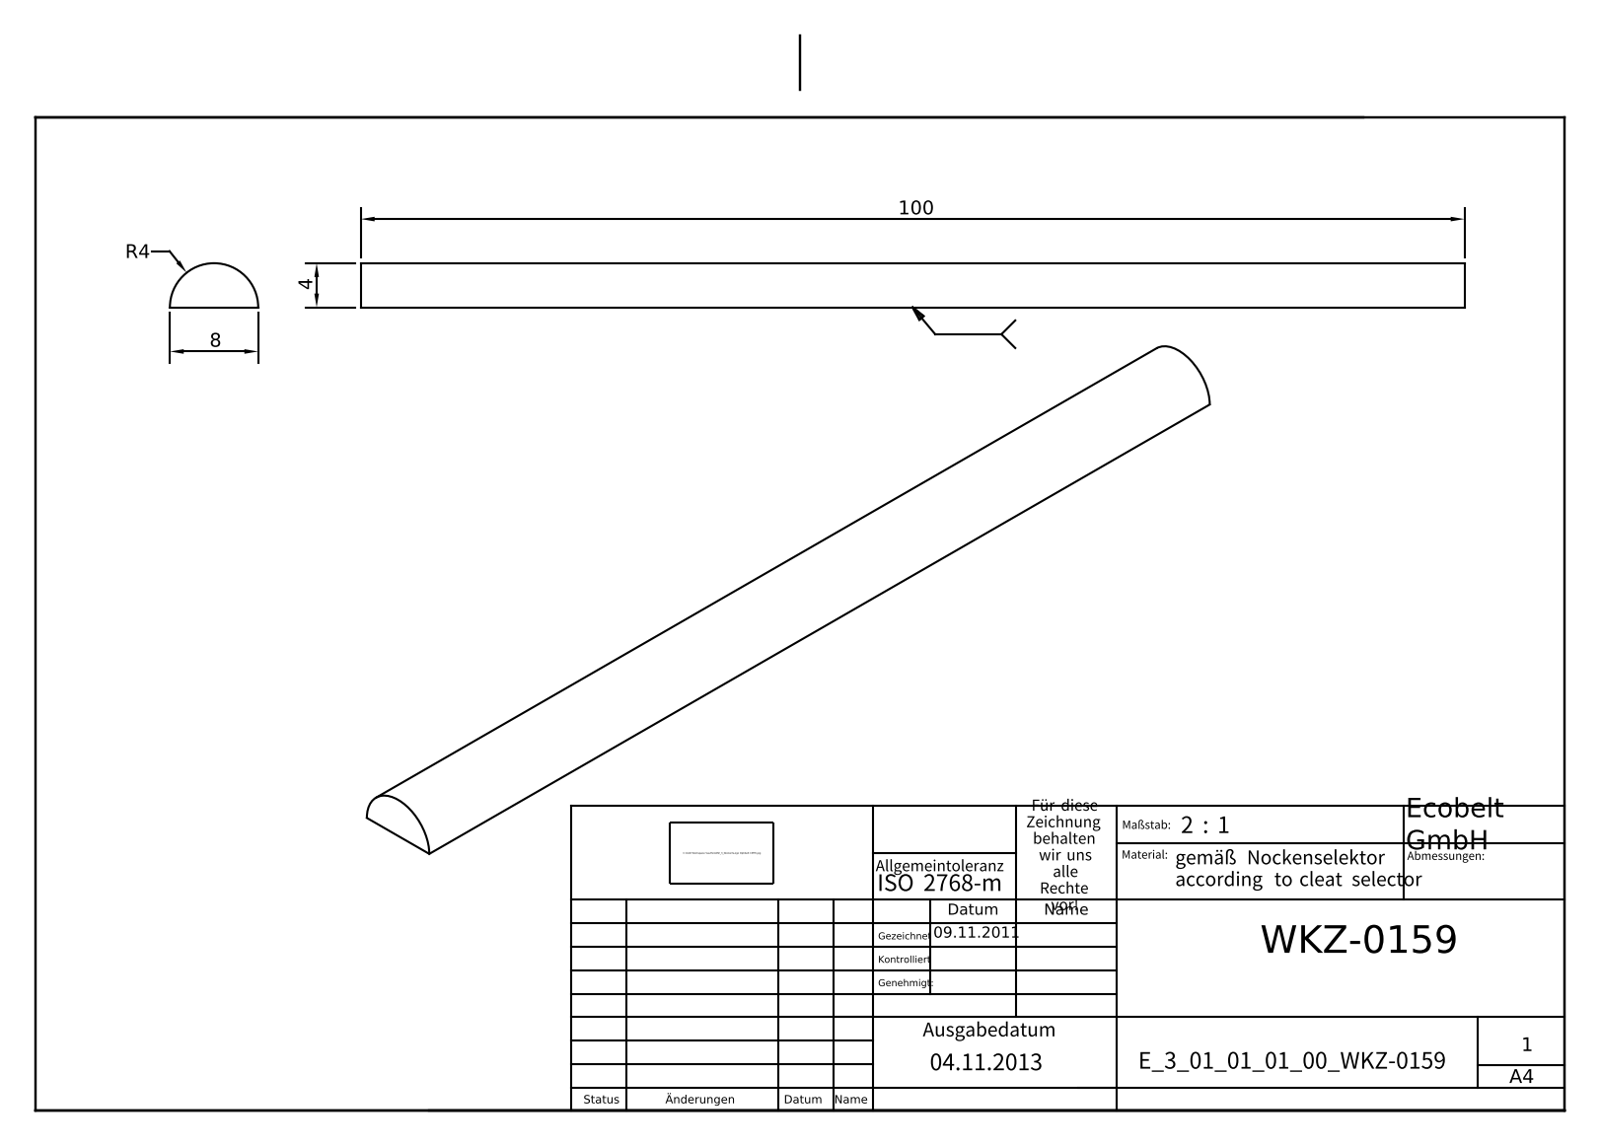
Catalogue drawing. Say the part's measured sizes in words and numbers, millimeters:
The part is named "E_3_01_01_01_00_WKZ-0159". Its 3-D file was written by "Autodesk Inventor 2021 (AUTOMOTIVE_DESIGN)". It is 1 solid with 4 faces: 3 planar, 1 cylindrical and 0 other. Overall it measures 100 by 8 by 4 millimeters. Its volume is 2 513 cubic millimeters and its surface area 2 107 square millimeters. Partial cylindrical surfaces (rounded edges, fillets, slot ends): 1 of radius 4. The main face-to-face distances are 100.
